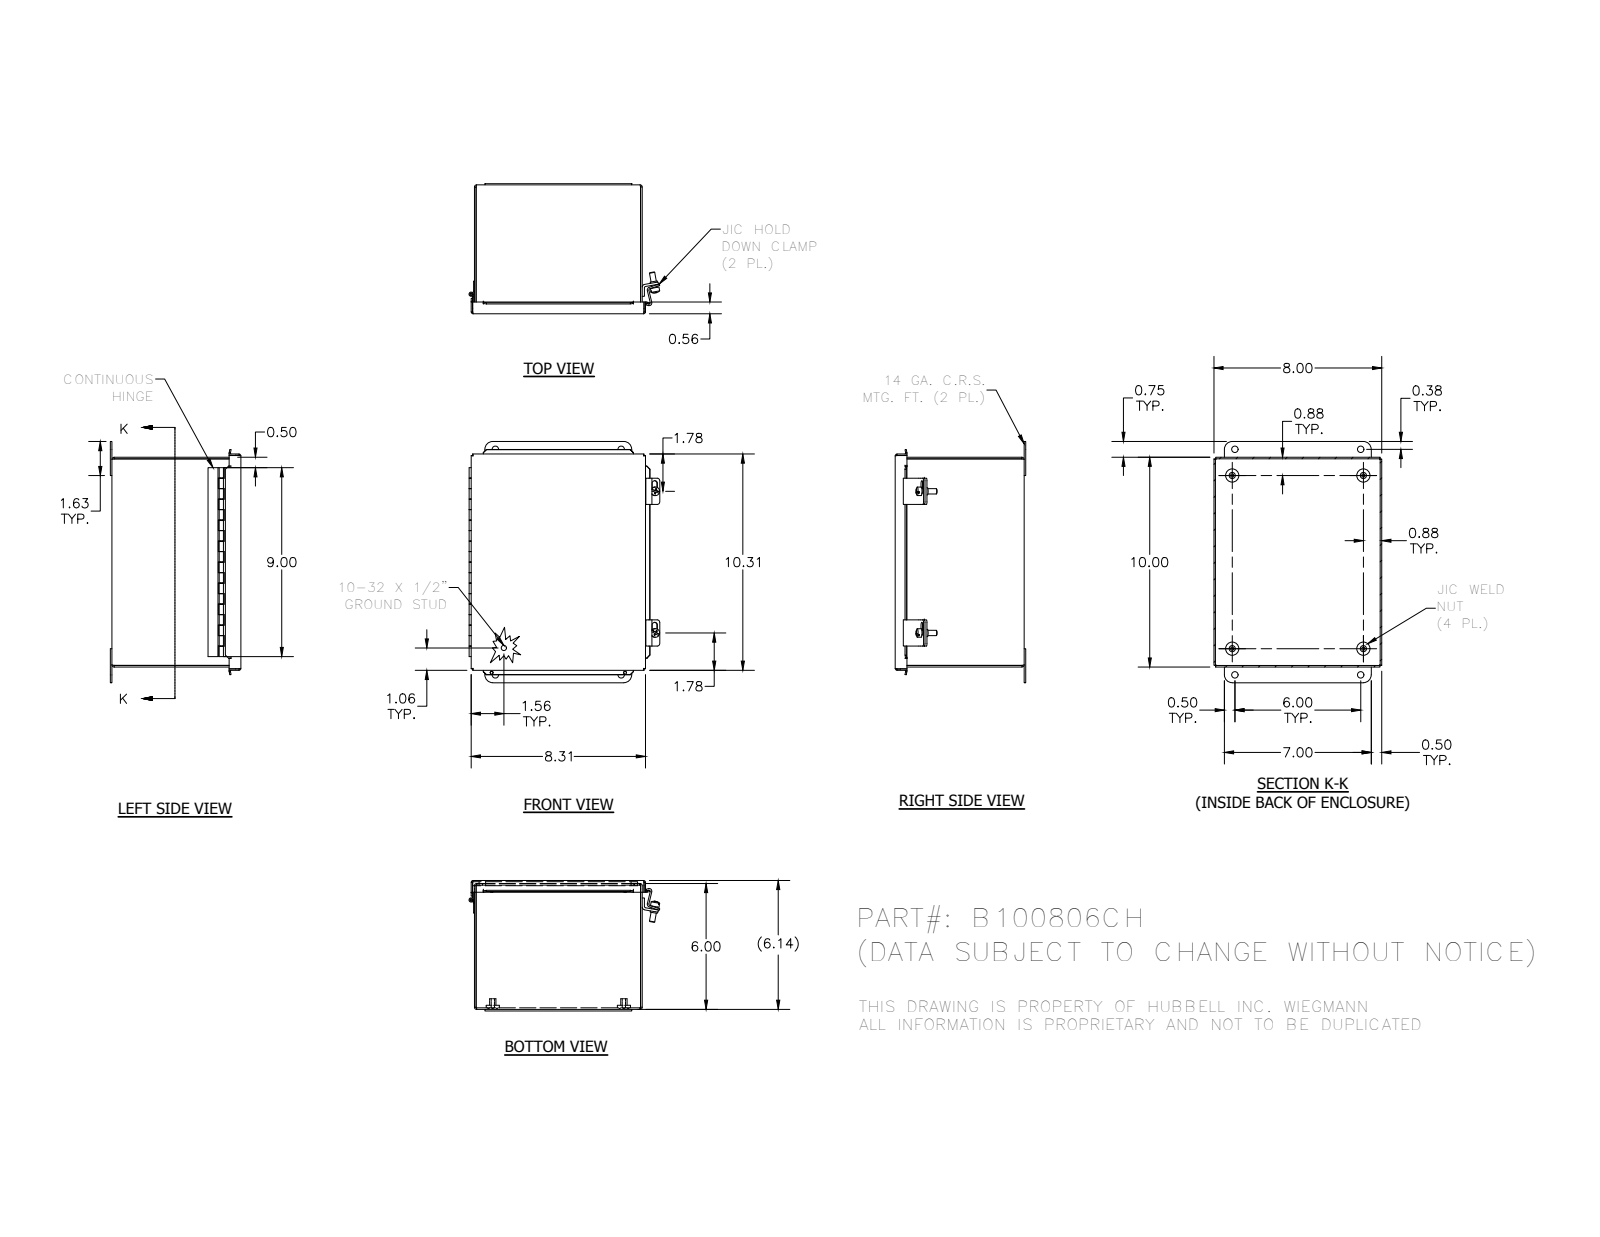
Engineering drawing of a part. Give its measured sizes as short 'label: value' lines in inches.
name: B100806CH; 3499; 3483; C1001 (+8 more)
written by: Autodesk Inventor 2012 (AUTOMOTIVE_DESIGN)
unit: in
bodies: 20 solids, 479 faces (311 planar, 123 cylindrical, 45 other)
size: 11.5 × 9.087 × 6.219
volume: 36.16 in³; area: 986.4 in²
holes: 4× ⌀0.156, 4× ⌀0.31, 2× ⌀0.14, 2× ⌀0.196, 1× ⌀0.116
bosses: 4× ⌀0.625, 4× ⌀0.3, 3× ⌀0.25, 2× ⌀0.41, 2× ⌀0.344, 1× ⌀0.2, 1× ⌀0.19, 1× ⌀0.1
rounds: 15× R0.031, 8× R0.105, 8× R0.125, 7× R0.093, 4× R0.133, 4× R0.375, 3× R0.063, 3× R0.126
face distances: 0.074, 7.926, 6.083, 9.926, 0.062, 6.144, 6.009, 6.07, 8, 7.852
hole spacings: 1.256, 9.501, 6, 6.25, 6.252, 8.25, 10.35, 11.304
